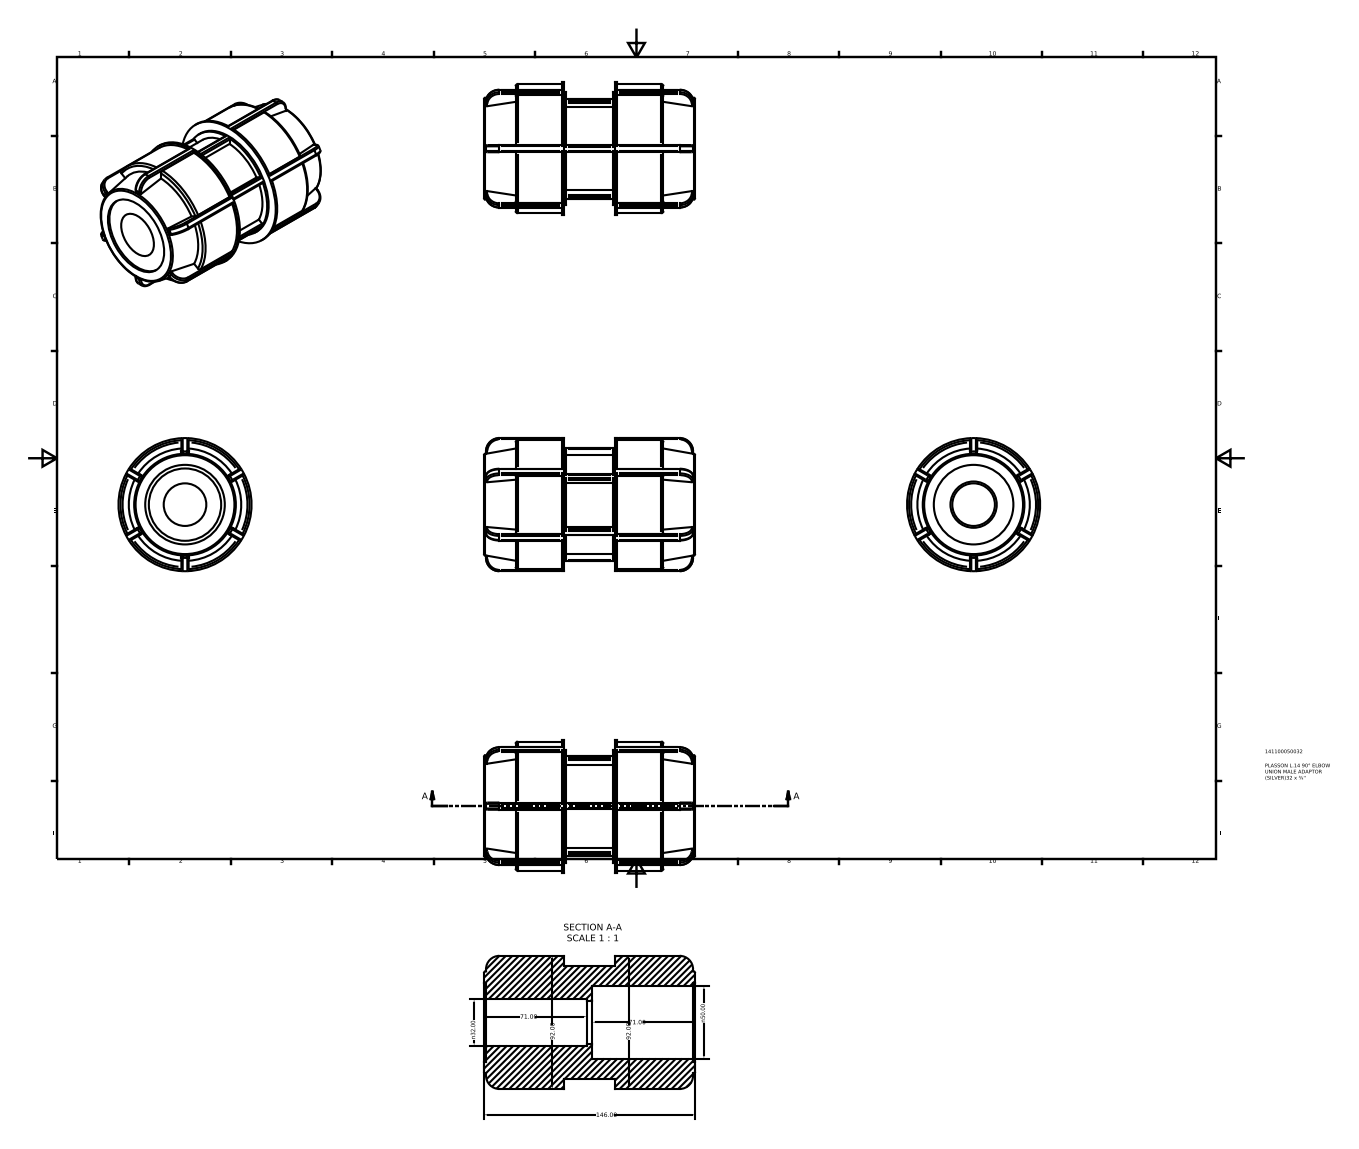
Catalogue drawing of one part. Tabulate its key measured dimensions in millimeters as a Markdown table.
| quantity | value |
| --- | --- |
| part name | 141100050032 |
| STEP written by | Autodesk Inventor 2015 (AUTOMOTIVE_DESIGN) |
| units | millimeters |
| bodies | 1 solid, 230 faces (92 planar, 86 cylindrical, 52 other) |
| overall size | 146 × 92 × 92 |
| volume | 557 093 mm³ |
| surface area | 77 037 mm² |
| round holes (diameter × count) | 29.44 × 1, 32 × 1, 50 × 1, 55 × 1 |
| round bosses / shafts (diameter × count) | 92 × 1, 89.24 × 1, 78.2 × 1, 69 × 1 |
| partial cylindrical surfaces (radius × count) | 0.92 × 36 |
| main face-to-face distances | 35.04, 1.46, 55.48, 89.06, 33.58, 90.52, 54.02, 21.9, 124.1, 68.62 |
